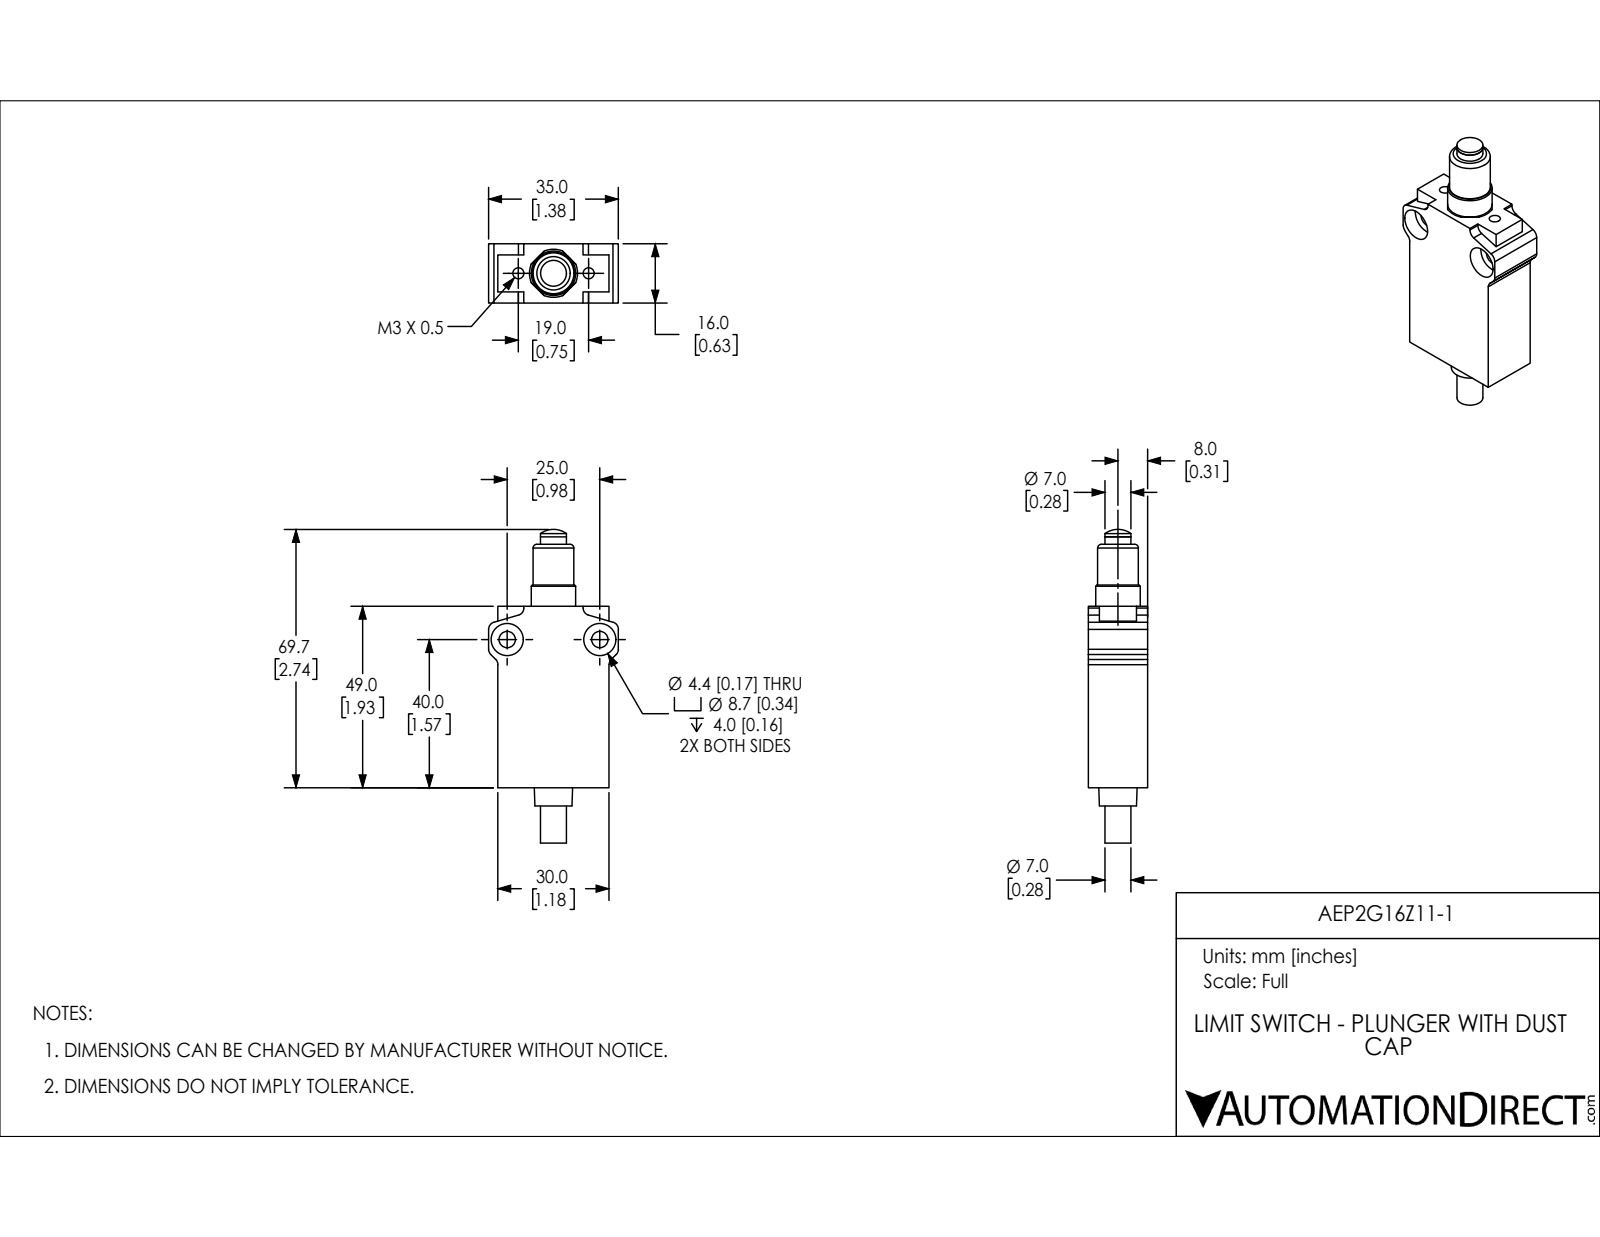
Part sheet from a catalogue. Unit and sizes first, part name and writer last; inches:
Units: inches
Overall size (bounding box): 3.331 × 1.378 × 0.63
Round holes (diameter × count): ⌀0.118 ×2, ⌀0.173 ×2, ⌀0.343 ×2, ⌀0.197 ×1, ⌀0.28 ×1
Round bosses / shafts (diameter × count): ⌀0.472 ×1, ⌀0.433 ×1, ⌀0.276 ×1
Partial cylindrical surfaces — rounded edges, fillets, slot ends (radius × count): R0.079 ×8, R0.256 ×1
Main face-to-face distances: 0.63, 1.181, 0.472, 1.929, 1.74, 0.189, 0.098, 0.157, 1.28, 0.039
Hole centre spacings: 0.374, 0.748, 0.984
Bodies: 0 solids, 131 faces (52 planar, 67 cylindrical, 12 other)
Part name (STEP PRODUCT): AEP2G16Z11-1
STEP written by: SolidWorks 2018 (AUTOMOTIVE_DESIGN)
